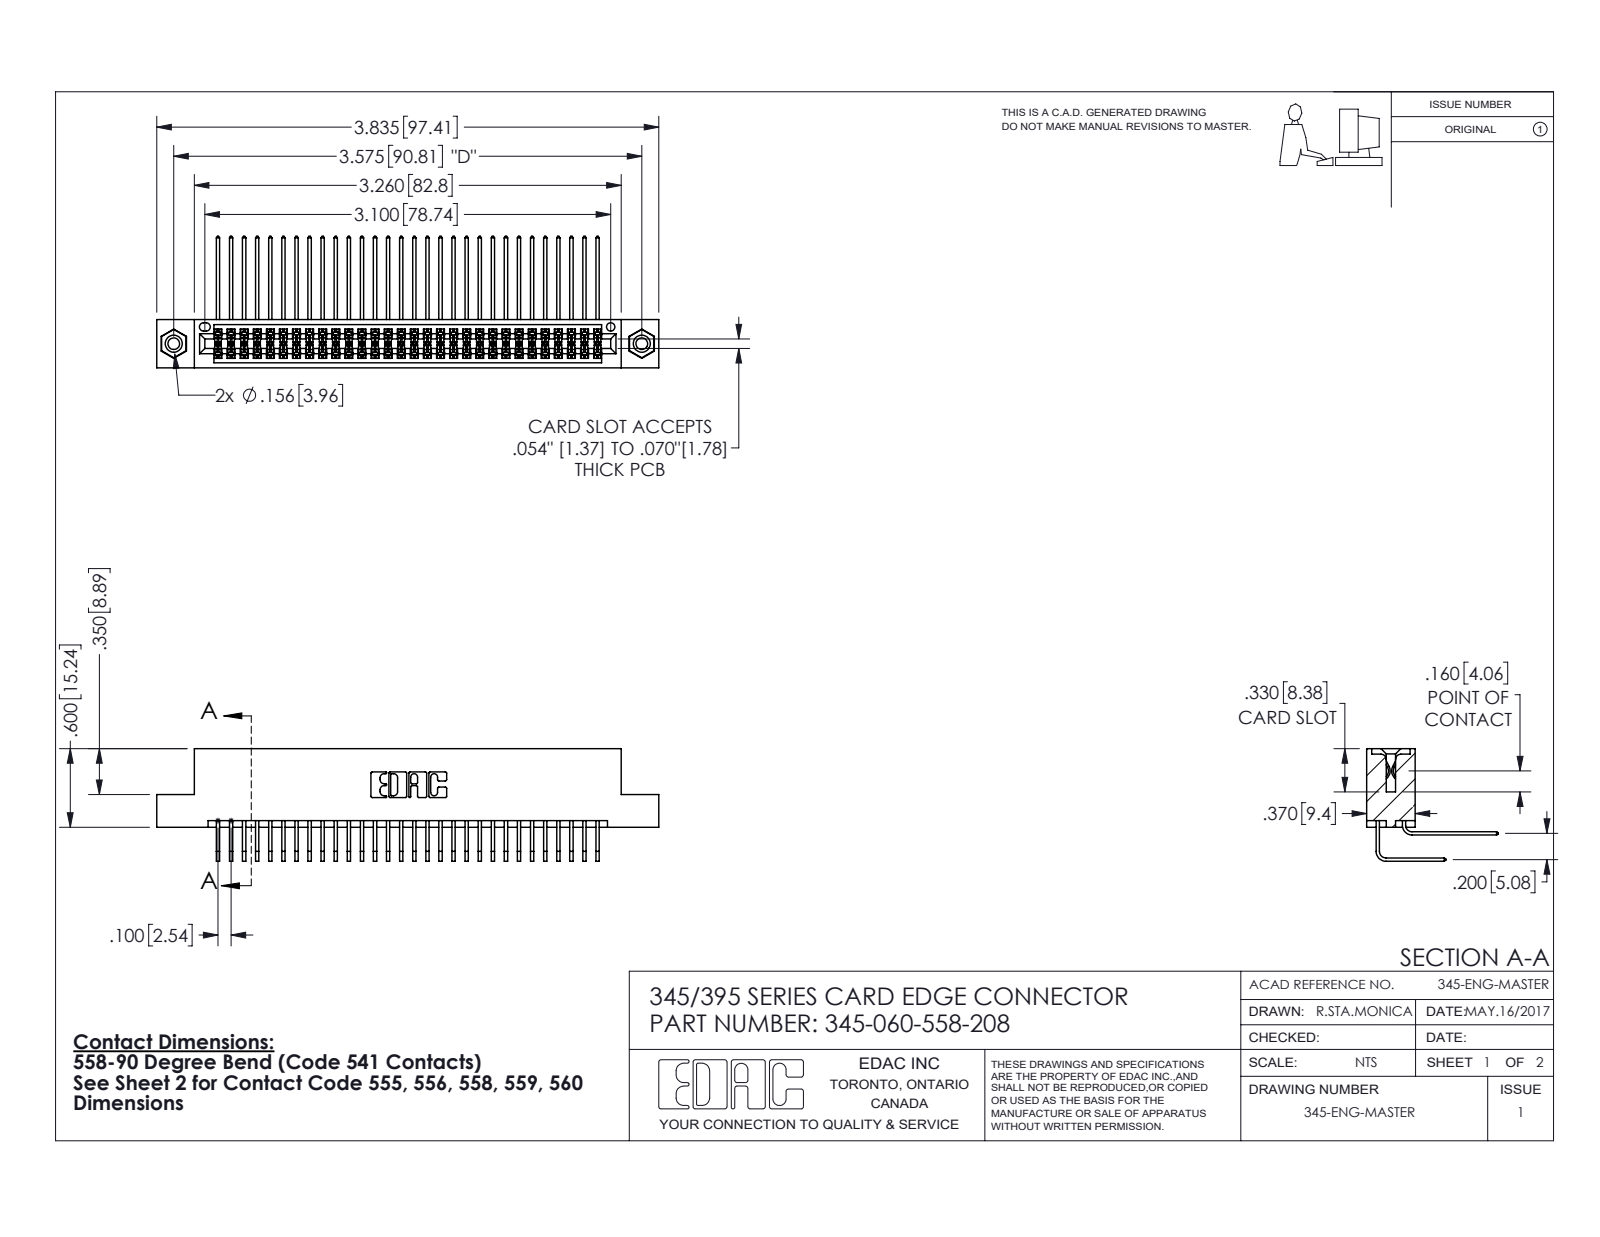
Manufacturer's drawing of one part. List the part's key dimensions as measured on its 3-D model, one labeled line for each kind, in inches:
Part name (STEP PRODUCT): 345-060-558-208; 345-292-001_558 559 Tail - 1; 345-250-001_345-250-003-102; 345-292-001_558 Tail - 2 (+1 more)
STEP written by: SolidWorks 2016 (CONFIG_CONTROL_DESIGN)
Units: inches
Bodies: 63 solids, 3306 faces (2212 planar, 1078 cylindrical, 16 other)
Overall size (bounding box): 3.835 × 1.005 × 0.859
Volume: 0.591 in³ · Surface area: 24.39 in²
Round holes (diameter × count): ⌀0.089 ×2, ⌀0.125 ×2, ⌀0.156 ×2, ⌀0.064 ×1
Round bosses / shafts (diameter × count): ⌀0.155 ×2
Partial cylindrical surfaces — rounded edges, fillets, slot ends (radius × count): R0.006 ×120, R0.01 ×22, R0.007 ×6, R0.031 ×6, R0.026 ×3, R0.014 ×2, R0.019 ×2, R0.022 ×2
Main face-to-face distances: 0.072, 0.298, 0.2, 0.37, 0.098, 0.272, 0.025, 0.225, 0.025, 0.175
Hole centre spacings: 0.27, 3.34, 3.575
